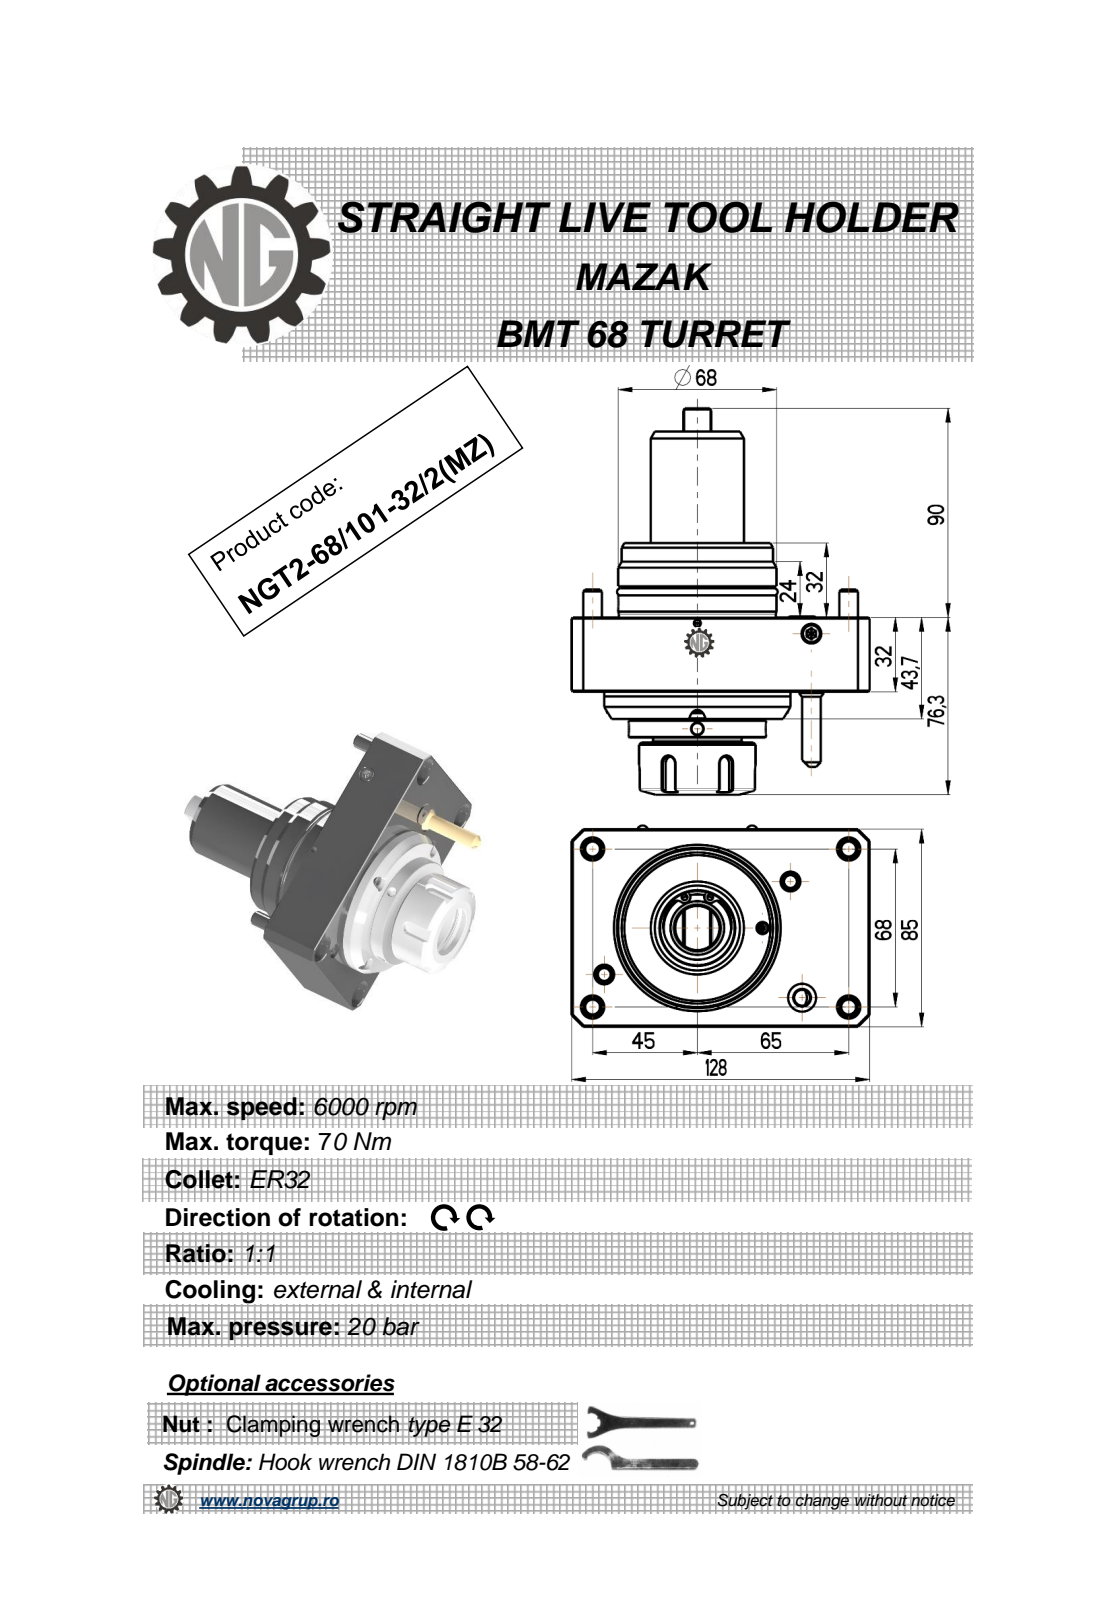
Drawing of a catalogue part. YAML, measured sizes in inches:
part_name: "NGT2_68_101_32_1_MZ"
step_written_by: "PRO/ENGINEER BY PARAMETRIC TECHNOLOGY CORPORATION, 2010280 (CONFIG_CONTROL_DESIGN)"
units: inches
bodies: {solids: 1, faces: 243, planar: 81, cylindrical: 71, other: 91}
overall_size: [6.547, 5.039, 3.409]
volume: 39.31
surface_area: 99.79
round_holes:
  - {diameter: 0.197, count: 3}
  - {diameter: 0.118, count: 1}
  - {diameter: 0.268, count: 1}
  - {diameter: 1.063, count: 1}
round_bosses_or_shafts:
  - {diameter: 0.315, count: 5}
  - {diameter: 3.15, count: 1}
  - {diameter: 2.677, count: 1}
  - {diameter: 2.559, count: 1}
  - {diameter: 2.48, count: 1}
  - {diameter: 2.323, count: 1}
  - {diameter: 1.969, count: 1}
  - {diameter: 1.89, count: 1}
partial_cylinders:
  - {radius: 0.009, count: 6}
  - {radius: 0.118, count: 5}
  - {radius: 0.138, count: 4}
  - {radius: 0.031, count: 2}
  - {radius: 0.394, count: 1}
face_to_face_distances: [1.26, 3.346, 1.72, 0.461, 5.039, 2.52, 2.98, 3.295, 2.035, 0.776]
hole_center_spacings: [1.192, 1.929, 2.129]
